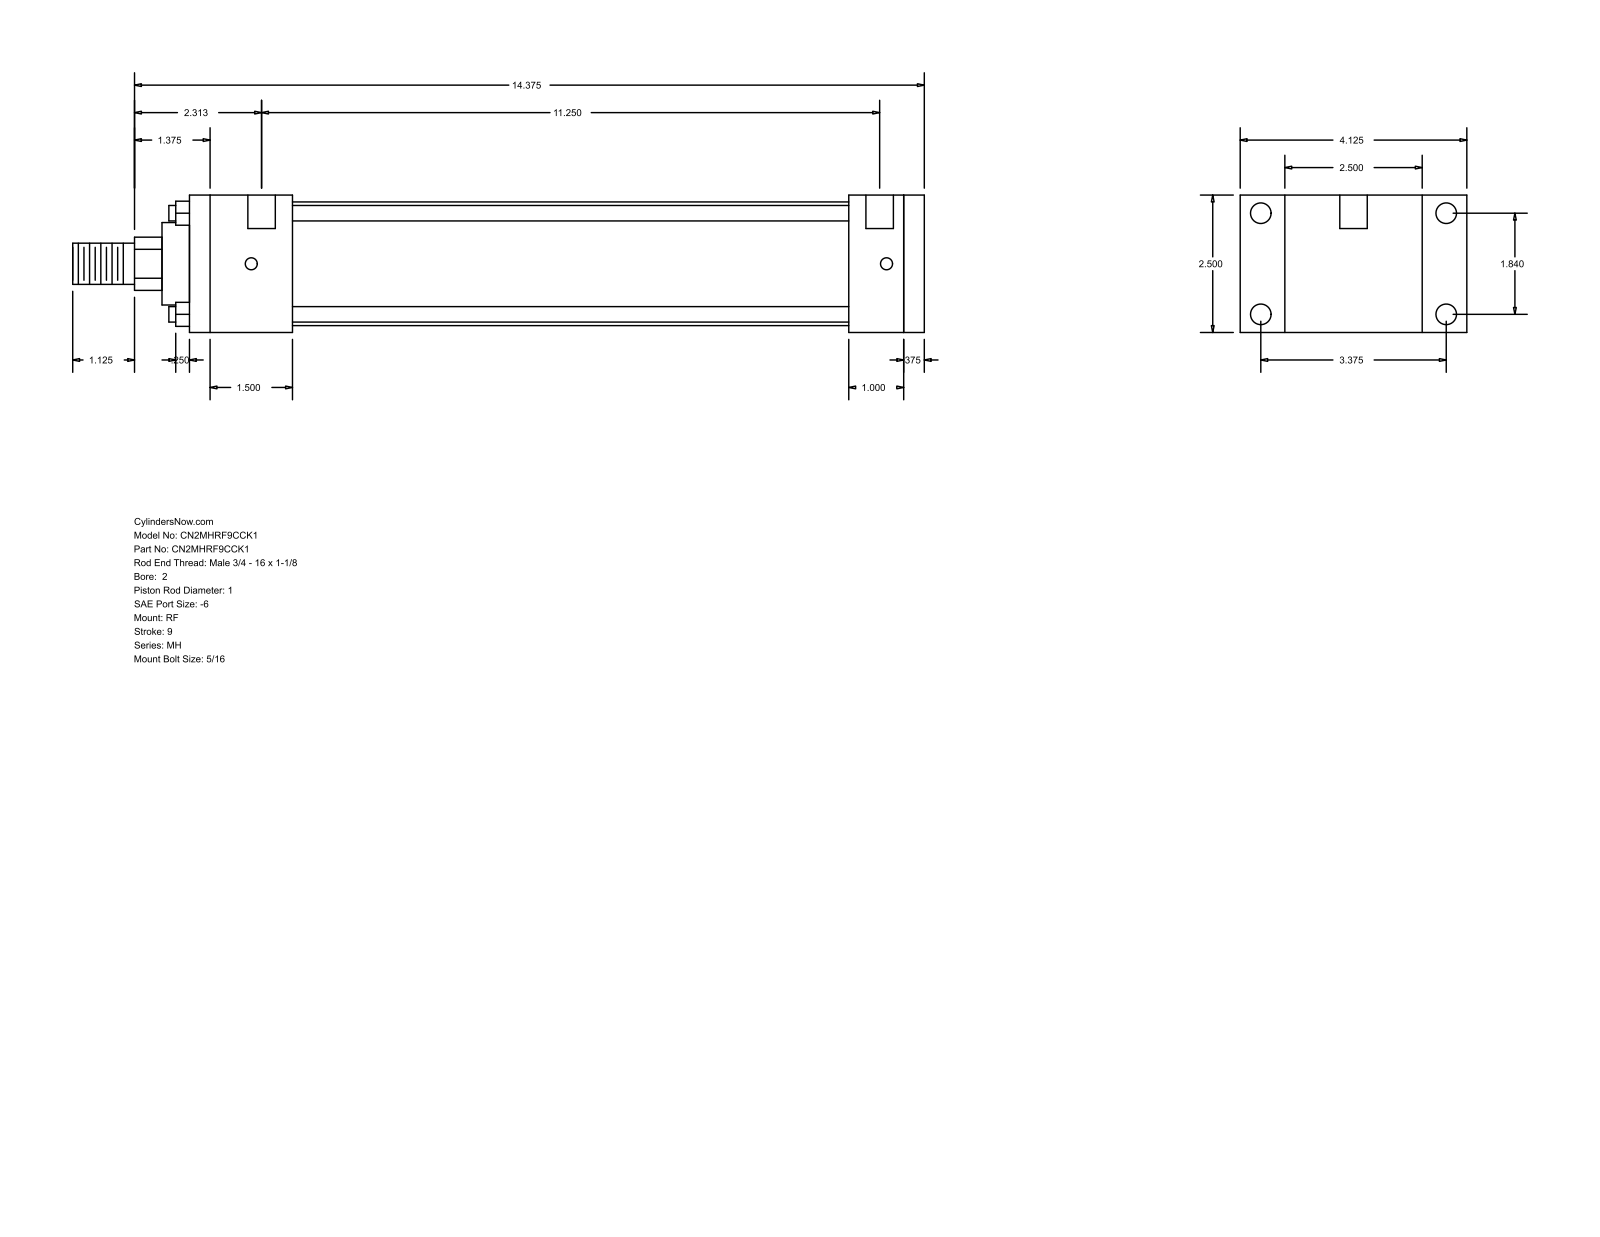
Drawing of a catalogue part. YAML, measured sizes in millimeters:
part_name: "MH_RF__0200_1"
step_written_by: "GSSL Pune (CONFIG_CONTROL_DESIGN)"
units: millimeters
bodies: {solids: 0, faces: 92, planar: 64, cylindrical: 28, other: 0}
overall_size: [393.7, 104.78, 63.5]
round_holes:
  - {diameter: 5.56, count: 4}
  - {diameter: 9.53, count: 4}
  - {diameter: 12.7, count: 2}
round_bosses_or_shafts:
  - {diameter: 7.14, count: 4}
  - {diameter: 57.15, count: 1}
  - {diameter: 38.1, count: 1}
  - {diameter: 25.4, count: 1}
  - {diameter: 19.05, count: 1}
partial_cylinders:
  - {radius: 12.29, count: 1}
face_to_face_distances: [63.5, 339.72, 9.52, 330.2, 20.64, 25.4, 47.63, 304.8, 257.17, 282.57]
hole_center_spacings: [46.74, 85.72, 97.63, 293.68, 3.17, 4.76, 285.75, 288.92]
